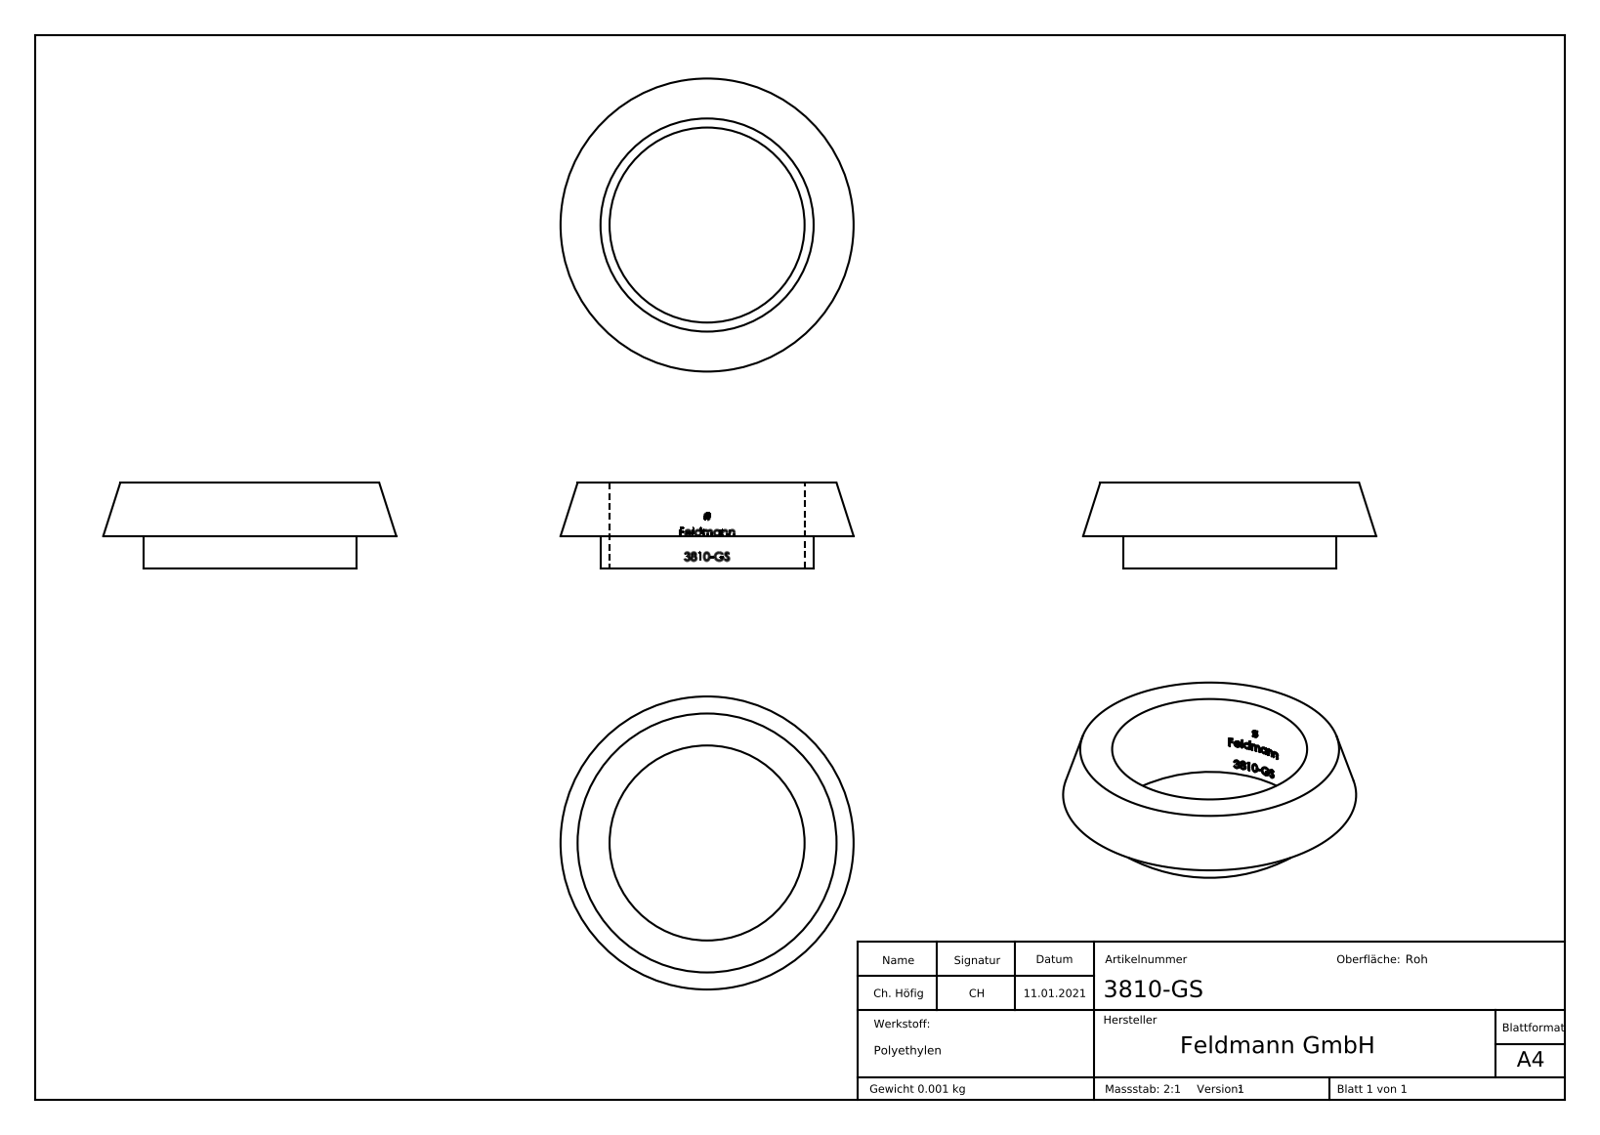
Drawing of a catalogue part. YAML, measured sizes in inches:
part_name: "3810-GS"
step_written_by: "SolidWorks 2018 (CONFIG_CONTROL_DESIGN)"
units: inches
bodies: {solids: 1, faces: 266, planar: 96, cylindrical: 36, other: 134}
overall_size: [1.083, 1.083, 0.315]
volume: 0.09
surface_area: 2.5
round_holes:
  - {diameter: 0.72, count: 1}
round_bosses_or_shafts:
  - {diameter: 0.787, count: 1}
partial_cylinders:
  - {radius: 0.364, count: 1}
face_to_face_distances: [0.197, 0.118, 0.315, 0.075, 0.109, 0.048, 0.07, 0.033, 0.096, 0.028]
